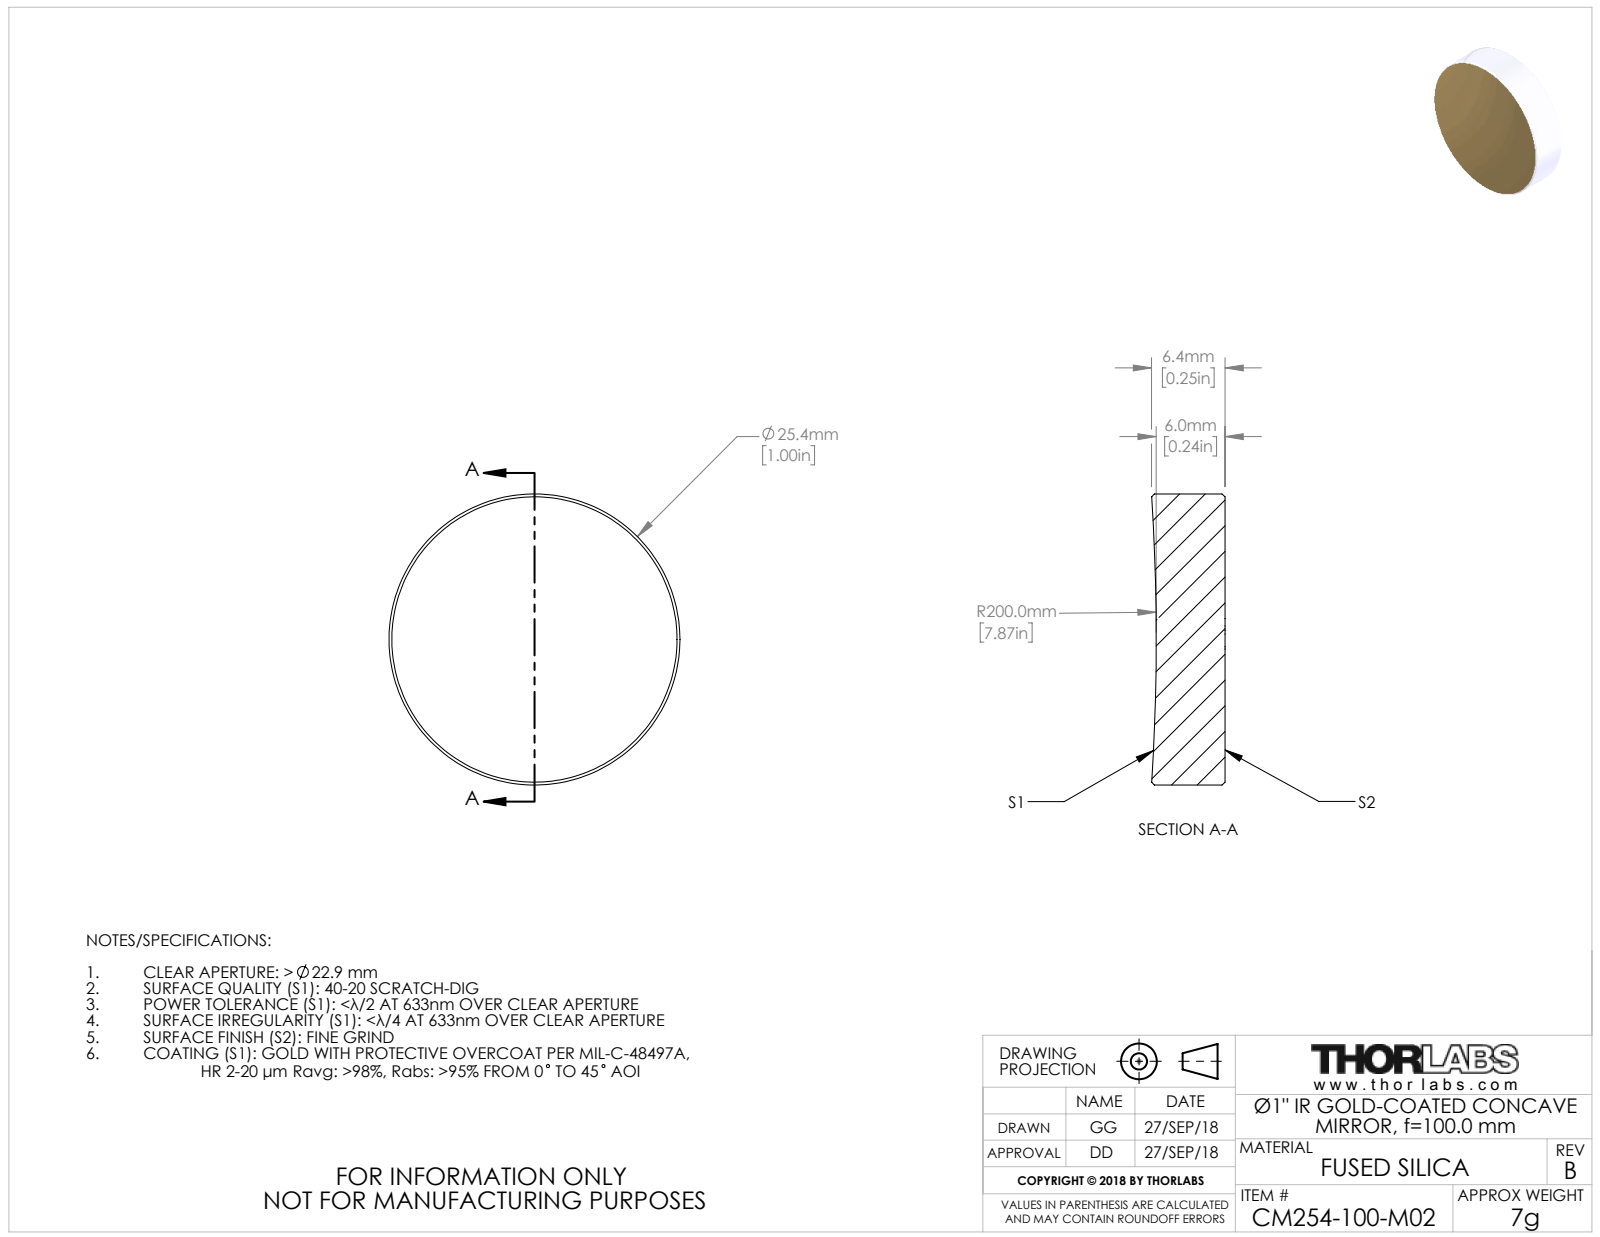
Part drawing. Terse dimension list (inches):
name: TTN028021-E0W
written by: SolidWorks 2014 (CONFIG_CONTROL_DESIGN)
unit: in
bodies: 1 solid, 39 faces (31 planar, 2 cylindrical, 6 other)
size: 1 × 1 × 0.251
volume: 0.191 in³; area: 2.326 in²
bosses: 1× ⌀1
